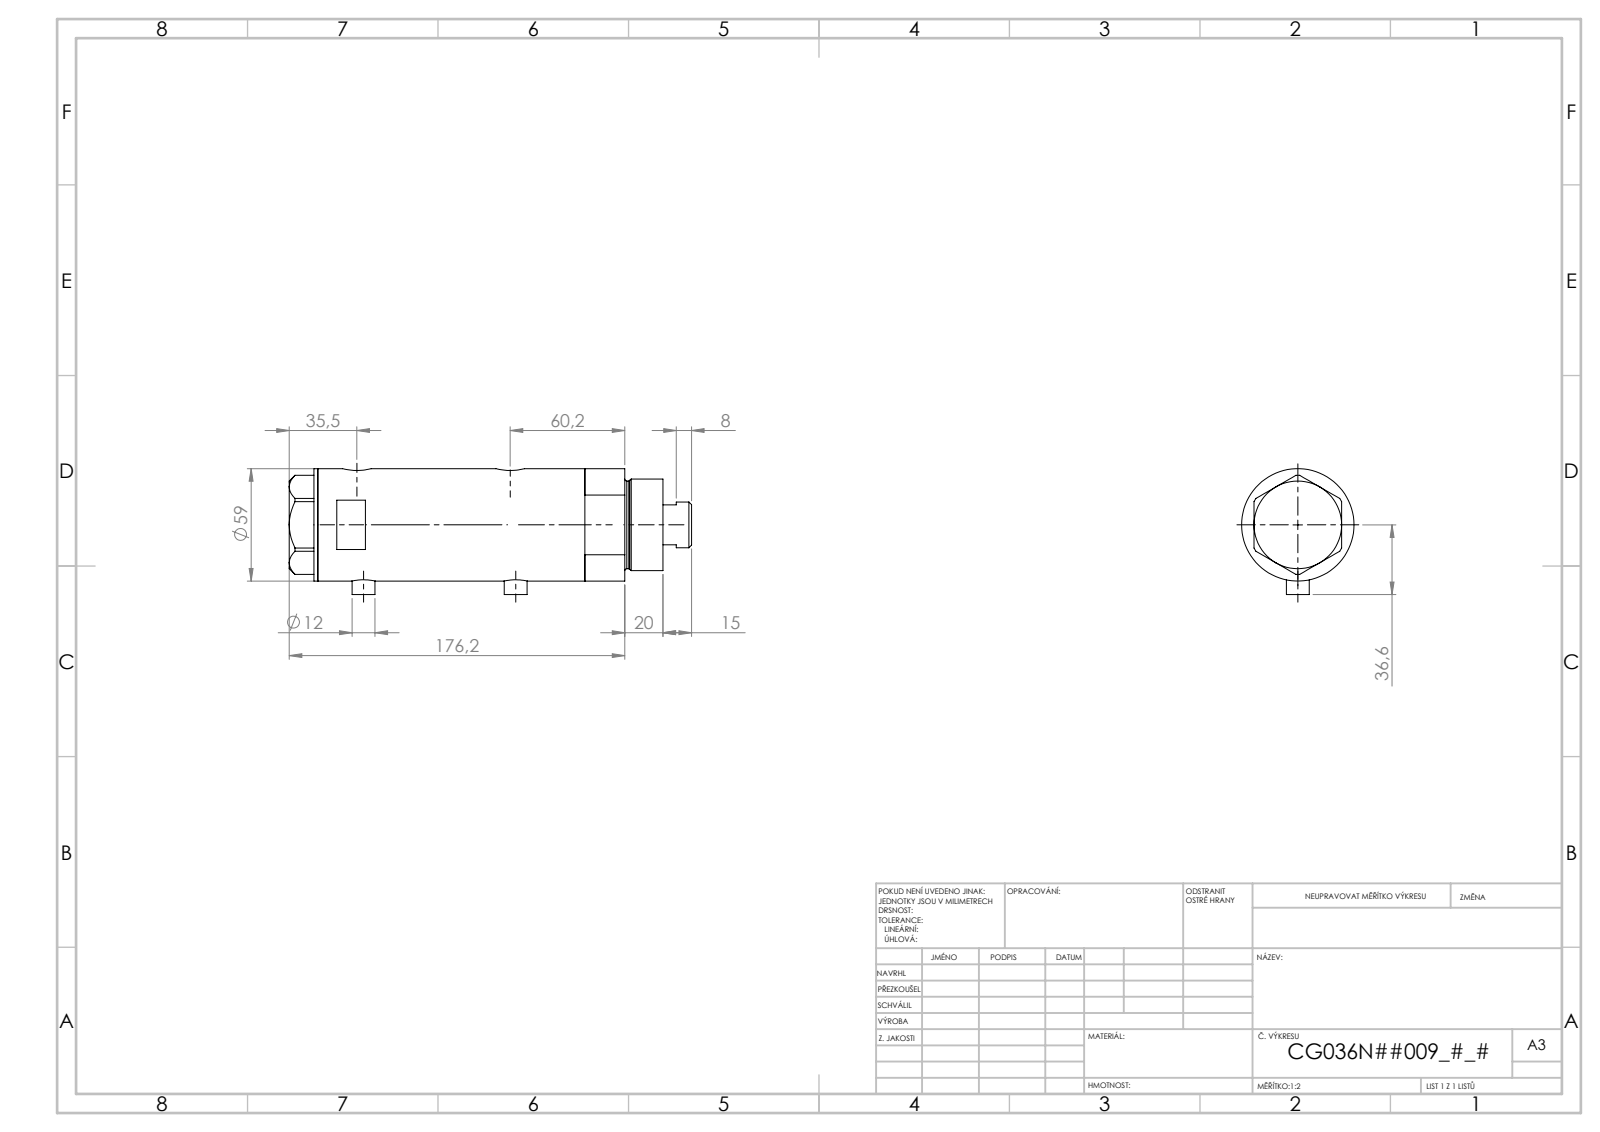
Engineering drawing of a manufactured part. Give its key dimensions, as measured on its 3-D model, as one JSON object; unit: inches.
{"part_name": "V270CG_VC; V270CG_BACK; V270CG_FRONT; V270CG_MIDDLE", "step_written_by": "SolidWorks 2019 (CONFIG_CONTROL_DESIGN)", "units": "inches", "bodies": {"solids": 4, "faces": 126, "planar": 53, "cylindrical": 53, "other": 20}, "overall_size": [6.788, 2.366, 2.323], "volume_in3": 23.86, "surface_area_in2": 132.2, "round_holes": [[0.197, 2], [0.383, 2], [0.492, 2], [0.591, 2], [0.335, 1], [0.984, 1], [1.043, 1], [1.417, 1], [1.575, 1], [2.047, 1]], "round_bosses_or_shafts": [[0.472, 2], [2.323, 1], [1.89, 1], [1.811, 1], [0.945, 1]], "face_to_face_distances": [2.612, 0.591, 1.516, 3.203, 1.687, 0.591, 0.925, 0.925, 2.612, 6.198], "hole_center_spacings": [0.114, 0.138, 1.62, 1.734, 1.758, 1.872, 0.114, 0.115]}
